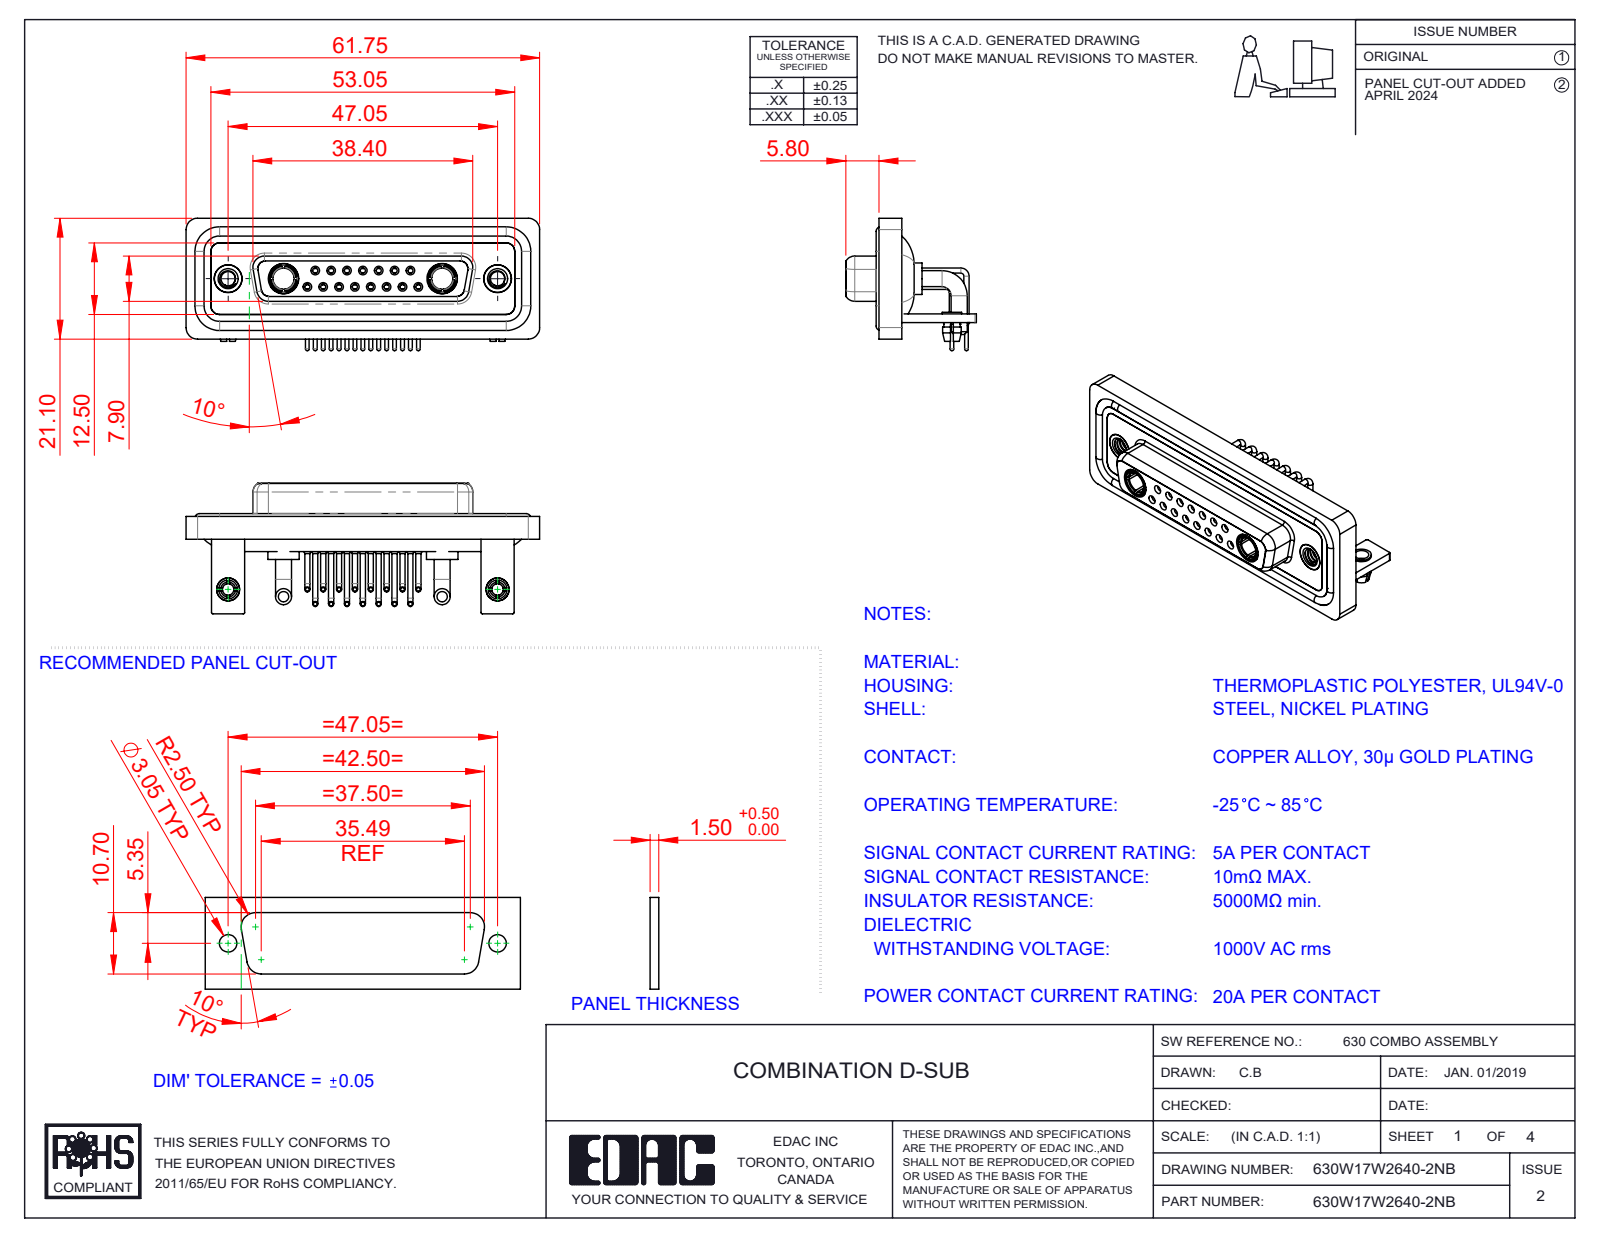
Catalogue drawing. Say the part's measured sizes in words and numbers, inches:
The part is named "630Combo Shell Front_25 Contacts; 630Combo Stabilizer Bracket_50 Contacts; 630Combo Contact Row 2_50 Contacts; 630W17W2640-2NB (+7 more)". Its 3-D file was written by "SolidWorks 2023 (CONFIG_CONTROL_DESIGN)". It is 30 solids with 1471 faces: 456 planar, 637 cylindrical and 378 other. Overall it measures 2.431 by 0.91 by 0.898 inches. Its volume is 0.542 cubic inches and its surface area 23.99 square inches. Round holes: 17 of diameter 0.079, 15 of diameter 0.035, 15 of diameter 0.043, 15 of diameter 0.059, 8 of diameter 0.063, 7 of diameter 0.067, 4 of diameter 0.098, 4 of diameter 0.191, 2 of diameter 0.126, 2 of diameter 0.146, 2 of diameter 0.157, 2 of diameter 0.159. Round bosses or shafts: 15 of diameter 0.035, 15 of diameter 0.026, 11 of diameter 0.063, 4 of diameter 0.11, 2 of diameter 0.217, 2 of diameter 0.205, 2 of diameter 0.195, 2 of diameter 0.195. Partial cylindrical surfaces (rounded edges, fillets, slot ends): 19 of radius 0.079, 18 of radius 0.059, 16 of radius 0.01, 8 of radius 0.053, 8 of radius 0.063, 5 of radius 0.02, 4 of radius 0.024, 4 of radius 0.026. The main face-to-face distances are 0.016, 0.071, 0.114, 0.146, 0.059, 0.161, 0.043, 0.055, 0.063, 0.122. The hole center spacings are 0.124, 0.109, 0.218, 0.327, 0.198, 0.295, 0.436, 0.198.
